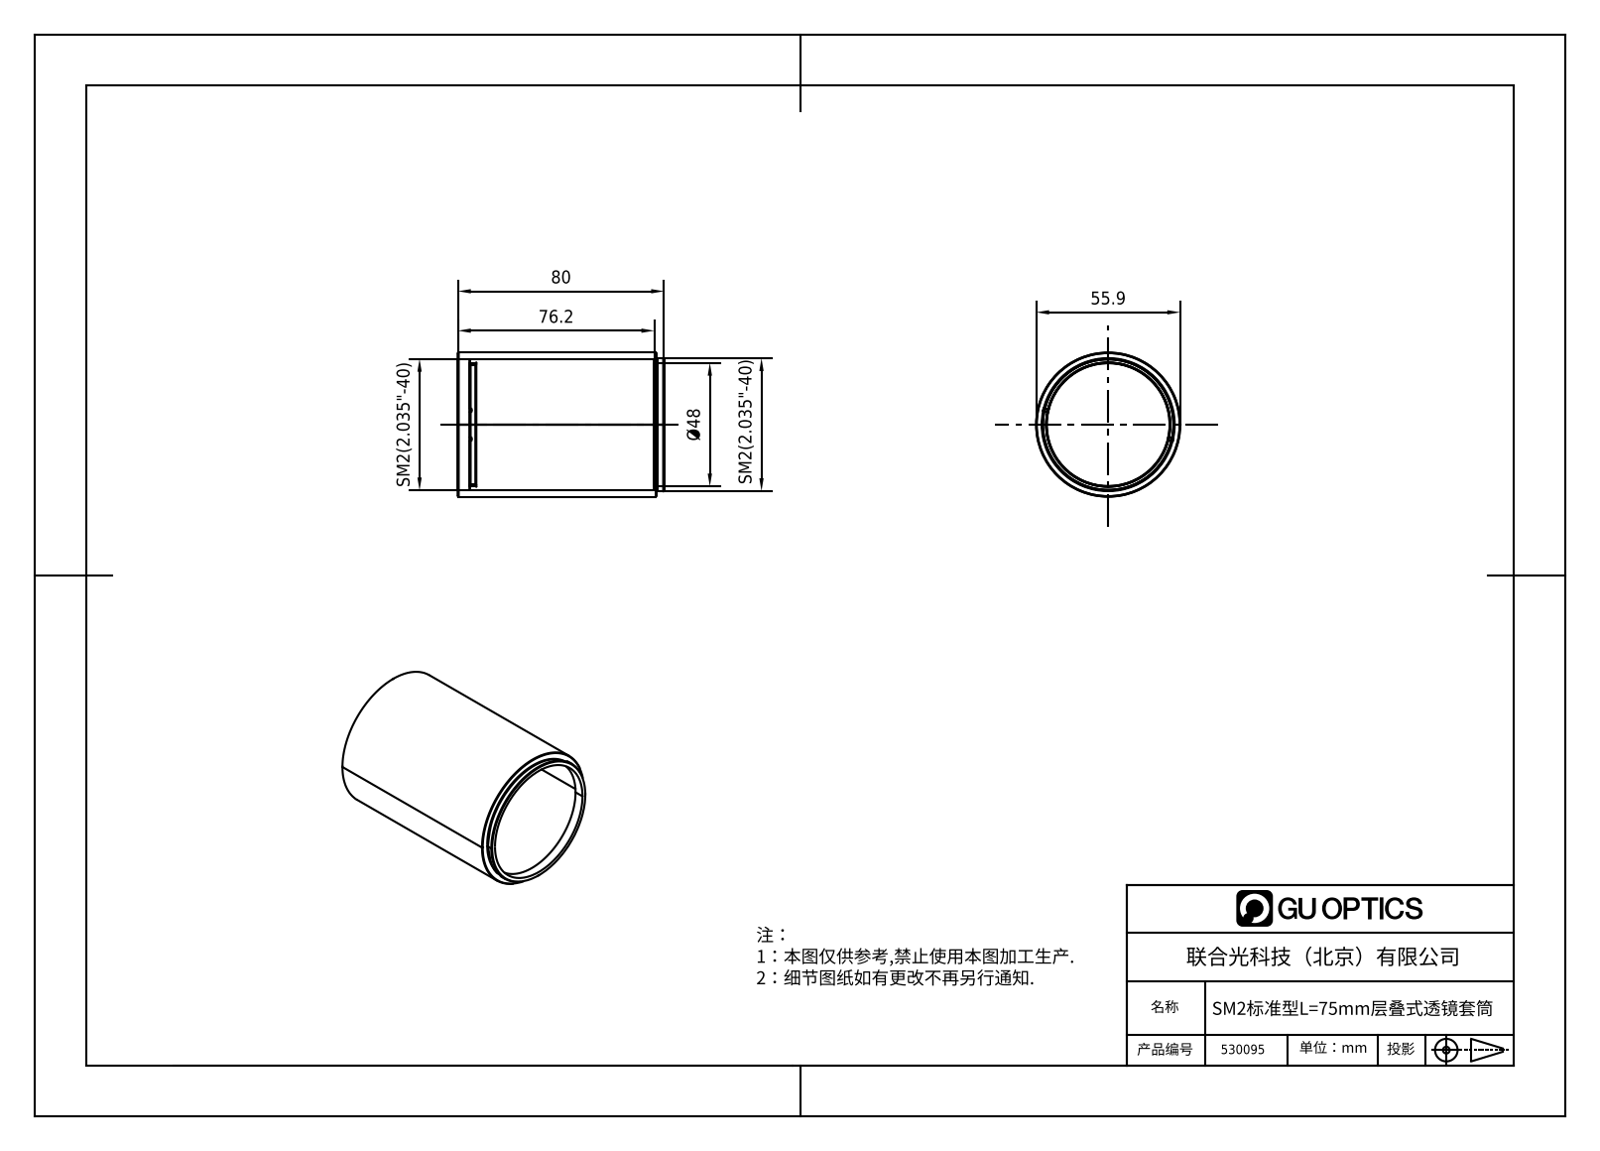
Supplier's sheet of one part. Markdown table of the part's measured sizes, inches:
| quantity | value |
| --- | --- |
| part name | 1.7.1.21_ZTC-2-3.0_SM2标准型3.0英寸层叠式透镜套筒 |
| STEP written by | SolidWorks 2018 (AUTOMOTIVE_DESIGN) |
| units | inches |
| bodies | 0 solids, 34 faces (11 planar, 12 cylindrical, 11 other) |
| overall size | 3.15 × 2.201 × 2.201 |
| round holes (diameter × count) | 1.878 × 1, 1.89 × 1, 2.01 × 1 |
| round bosses / shafts (diameter × count) | 2.201 × 1, 2.031 × 1, 1.992 × 1 |
| main face-to-face distances | 3.031, 3.15, 0.118, 0.181, 2.851, 2.969, 0.208, 0.028, 2.823, 2.941 |
